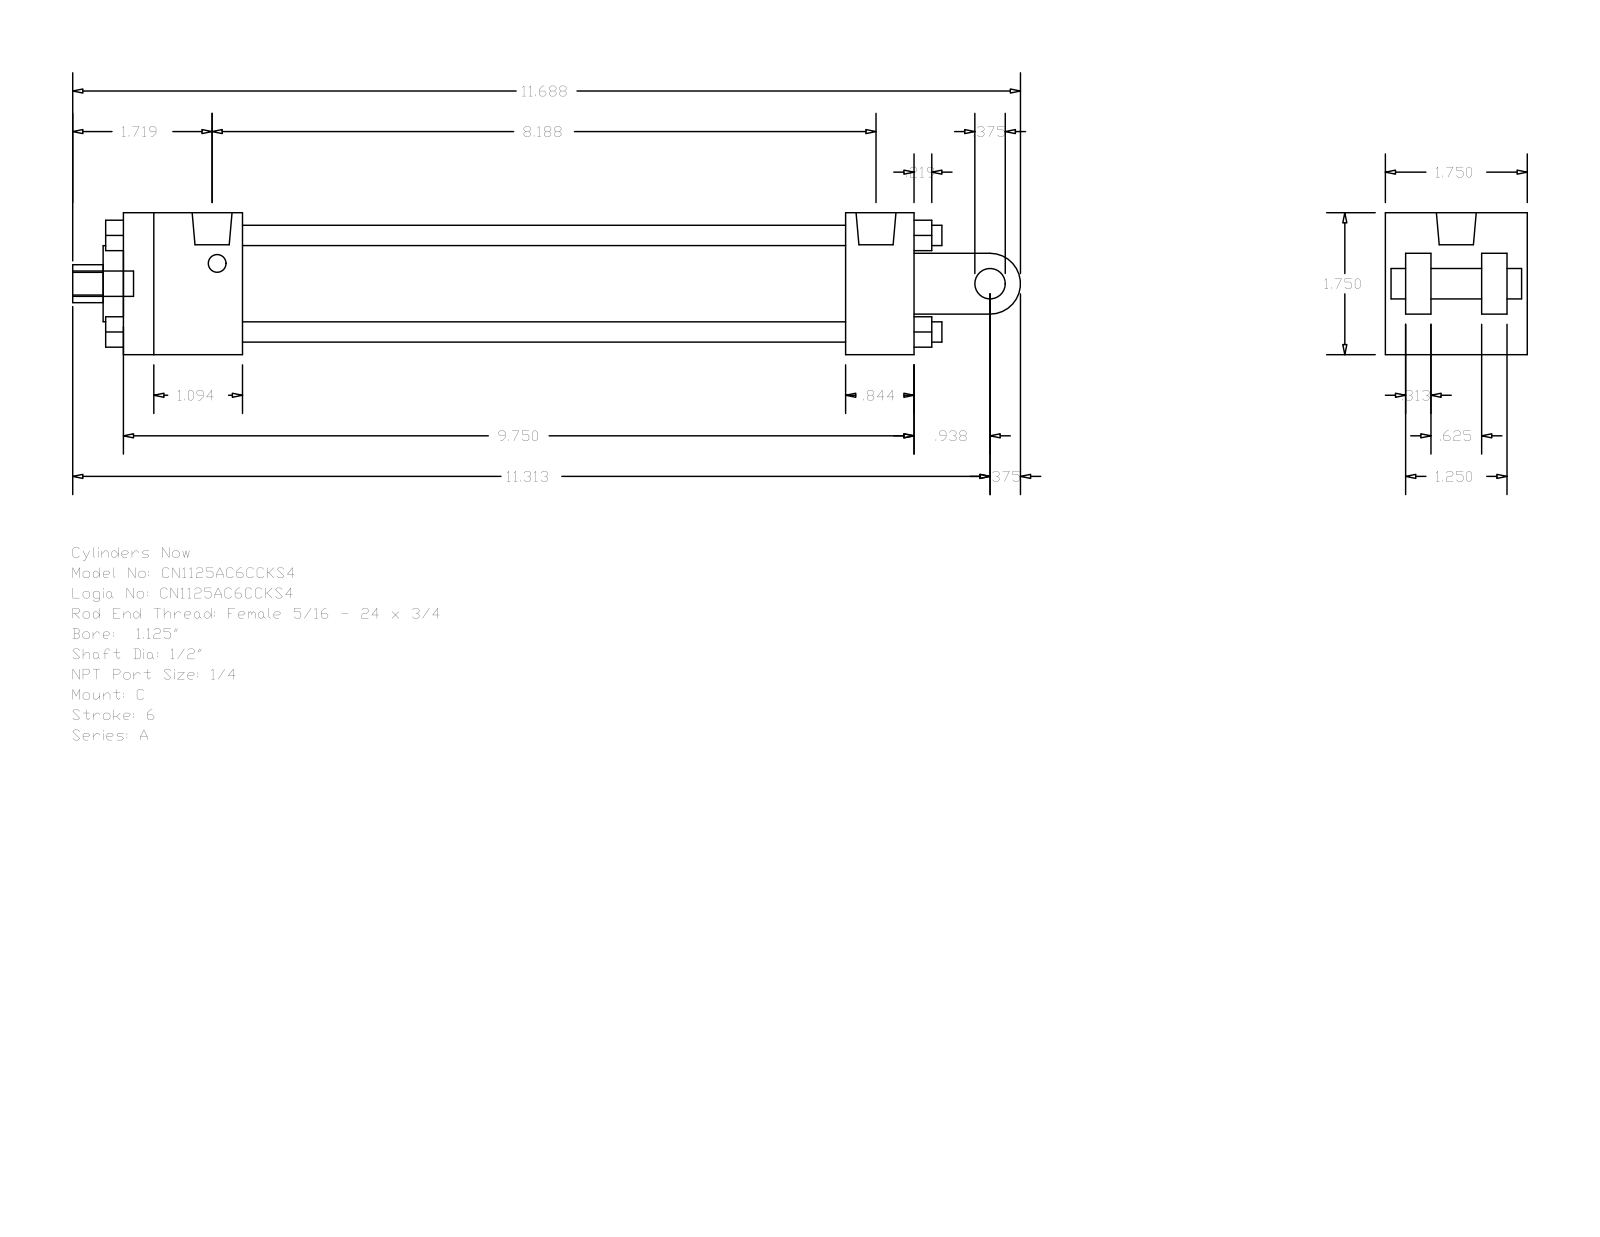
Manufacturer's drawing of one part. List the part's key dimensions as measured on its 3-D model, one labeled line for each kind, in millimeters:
Part name (STEP PRODUCT): A_C__0112_0.5
STEP written by: GSSL Pune (CONFIG_CONTROL_DESIGN)
Units: millimetres
Bodies: 0 solids, 135 faces (102 planar, 33 cylindrical, 0 other)
Overall size (bounding box): 296.86 × 44.45 × 44.45
Round holes (diameter × count): ⌀5.56 ×2, ⌀12.49 ×1, ⌀12.7 ×1, ⌀23.81 ×1, ⌀31.88 ×1
Round bosses / shafts (diameter × count): ⌀6.35 ×4, ⌀5.56 ×2, ⌀12.49 ×1, ⌀9.53 ×1, ⌀7.94 ×1
Partial cylindrical surfaces — rounded edges, fillets, slot ends (radius × count): R5.94 ×1, R9.53 ×1
Main face-to-face distances: 44.46, 6.35, 31.76, 14.29, 247.64, 30.17, 226.21, 21.43, 37.3, 188.91
Hole centre spacings: 1.59
